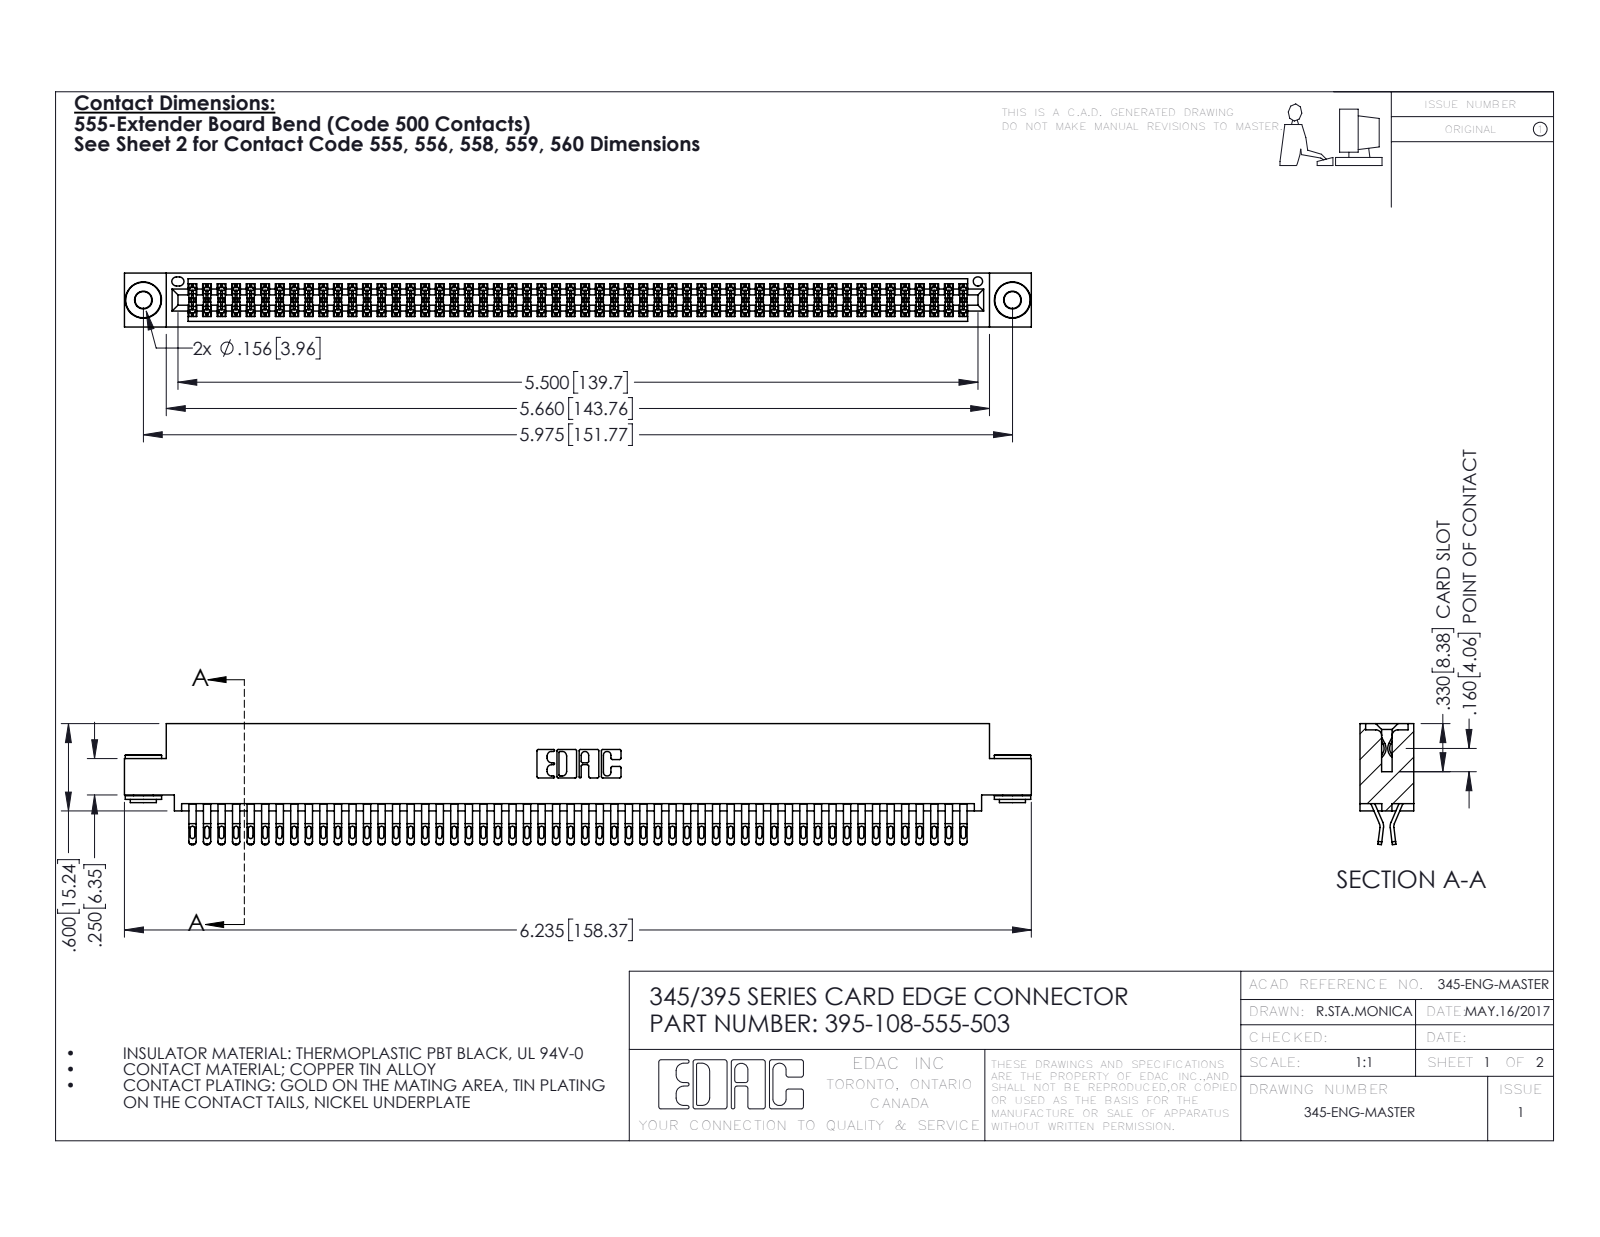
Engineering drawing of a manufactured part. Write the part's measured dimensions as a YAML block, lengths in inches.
part_name: "345 Part_0.110 Offset - 0.156 Dia-TH; 345-250-002_345-250-002-102; 345-292-001_555 Tail; 395-108-555-503"
step_written_by: "SolidWorks 2016 (CONFIG_CONTROL_DESIGN)"
units: inches
bodies: {solids: 111, faces: 6216, planar: 3442, cylindrical: 2766, other: 8}
overall_size: [6.235, 0.832, 0.37]
volume: 0.961
surface_area: 38.61
round_holes:
  - {diameter: 0.116, count: 2}
  - {diameter: 0.156, count: 2}
  - {diameter: 0.064, count: 1}
round_bosses_or_shafts:
  - {diameter: 0.25, count: 2}
  - {diameter: 0.18, count: 2}
  - {diameter: 0.136, count: 2}
partial_cylinders:
  - {radius: 0.016, count: 270}
  - {radius: 0.02, count: 216}
  - {radius: 0.006, count: 162}
  - {radius: 0.01, count: 22}
  - {radius: 0.007, count: 6}
  - {radius: 0.031, count: 6}
  - {radius: 0.026, count: 3}
  - {radius: 0.01, count: 2}
face_to_face_distances: [0.072, 0.298, 0.025, 0.37, 0.2, 0.098, 0.272, 0.225, 0.175, 0.149]
hole_center_spacings: [0.27, 5.739, 5.975]
